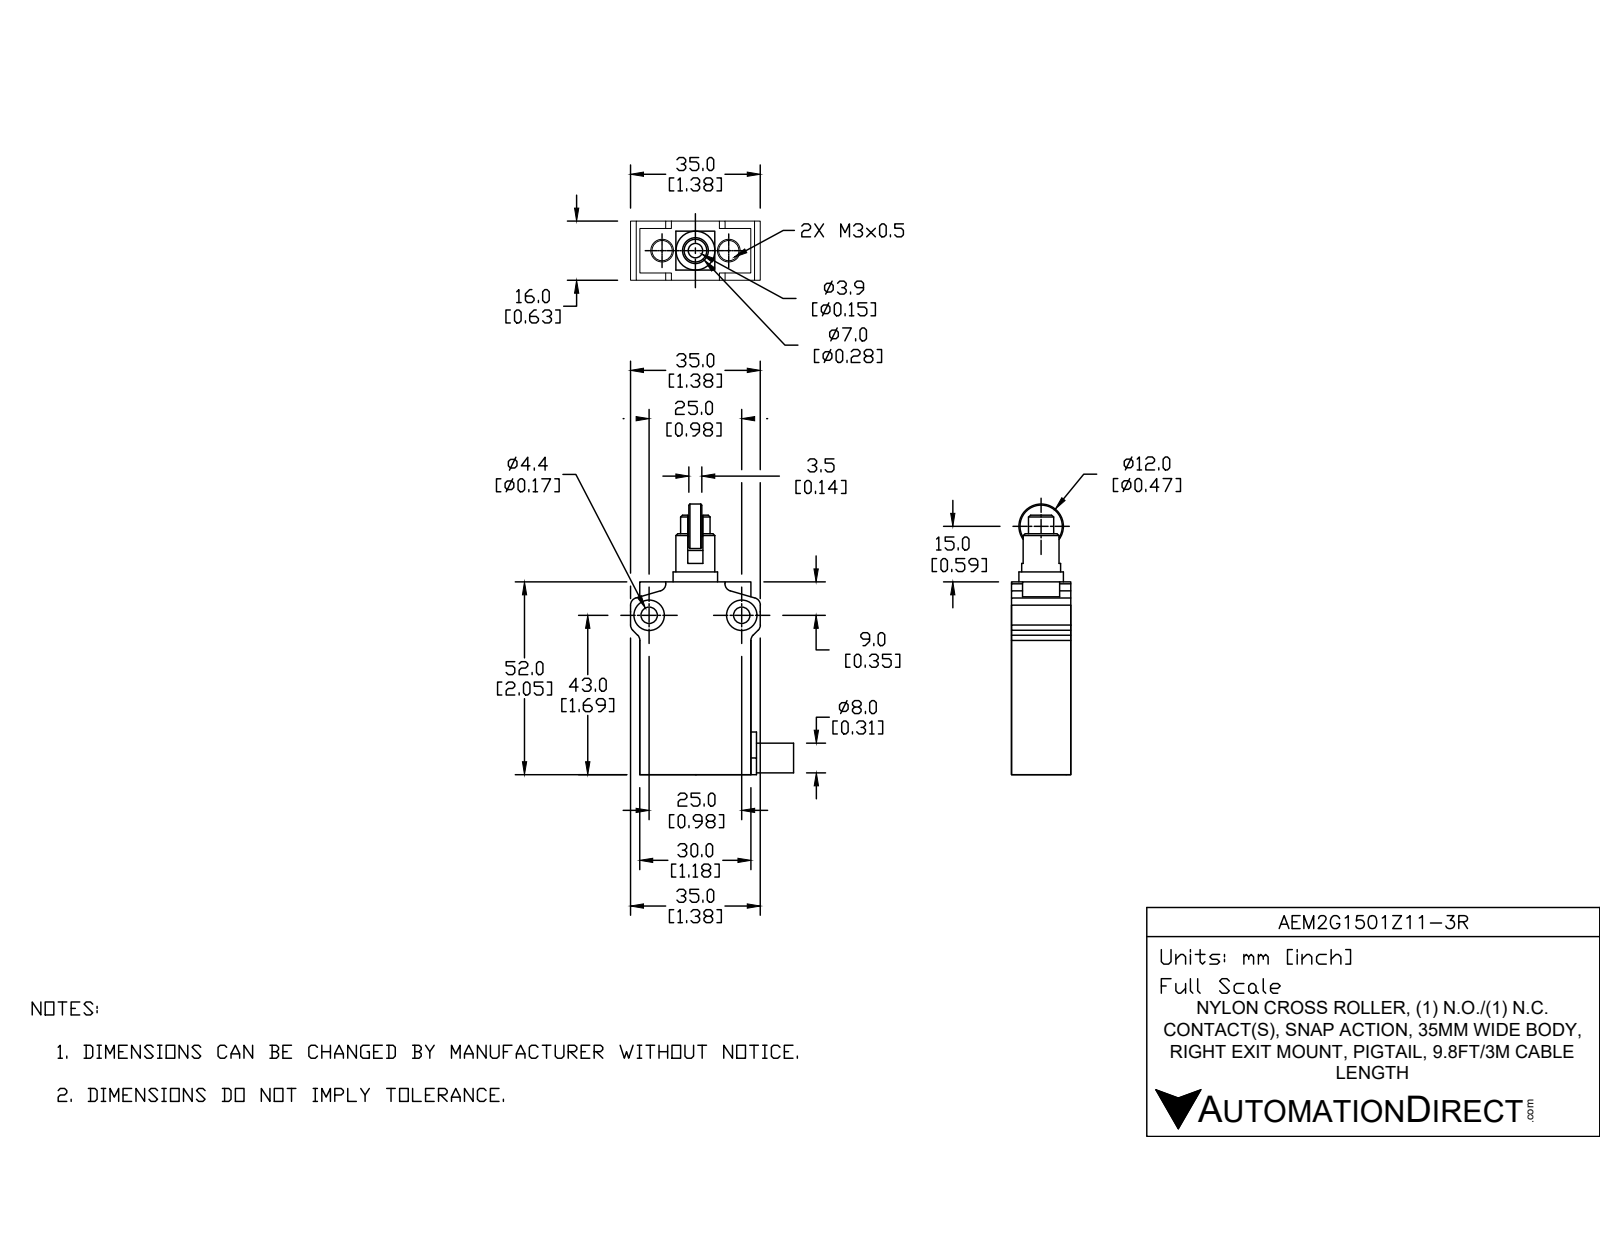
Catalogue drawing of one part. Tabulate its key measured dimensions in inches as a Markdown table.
| quantity | value |
| --- | --- |
| part name | AEM2G1501Z11-3R |
| STEP written by | SolidWorks 2017 (AUTOMOTIVE_DESIGN) |
| units | inches |
| bodies | 5 solids, 129 faces (64 planar, 52 cylindrical, 13 other) |
| overall size | 2.756 × 1.87 × 0.63 |
| volume | 1.516 in³ |
| surface area | 14.04 in² |
| round holes (diameter × count) | 0.118 × 2, 0.173 × 2, 0.323 × 2, 0.317 × 1 |
| round bosses / shafts (diameter × count) | 0.472 × 2, 0.413 × 1, 0.323 × 1, 0.313 × 1, 0.22 × 1 |
| partial cylindrical surfaces (radius × count) | 0.079 × 8, 0.256 × 1 |
| main face-to-face distances | 0.63, 1.181, 1.929, 0.472, 1.74, 0.189, 0.15, 0.157, 0.51, 0.671 |
| hole center spacings | 0.374, 0.748, 0.984 |
